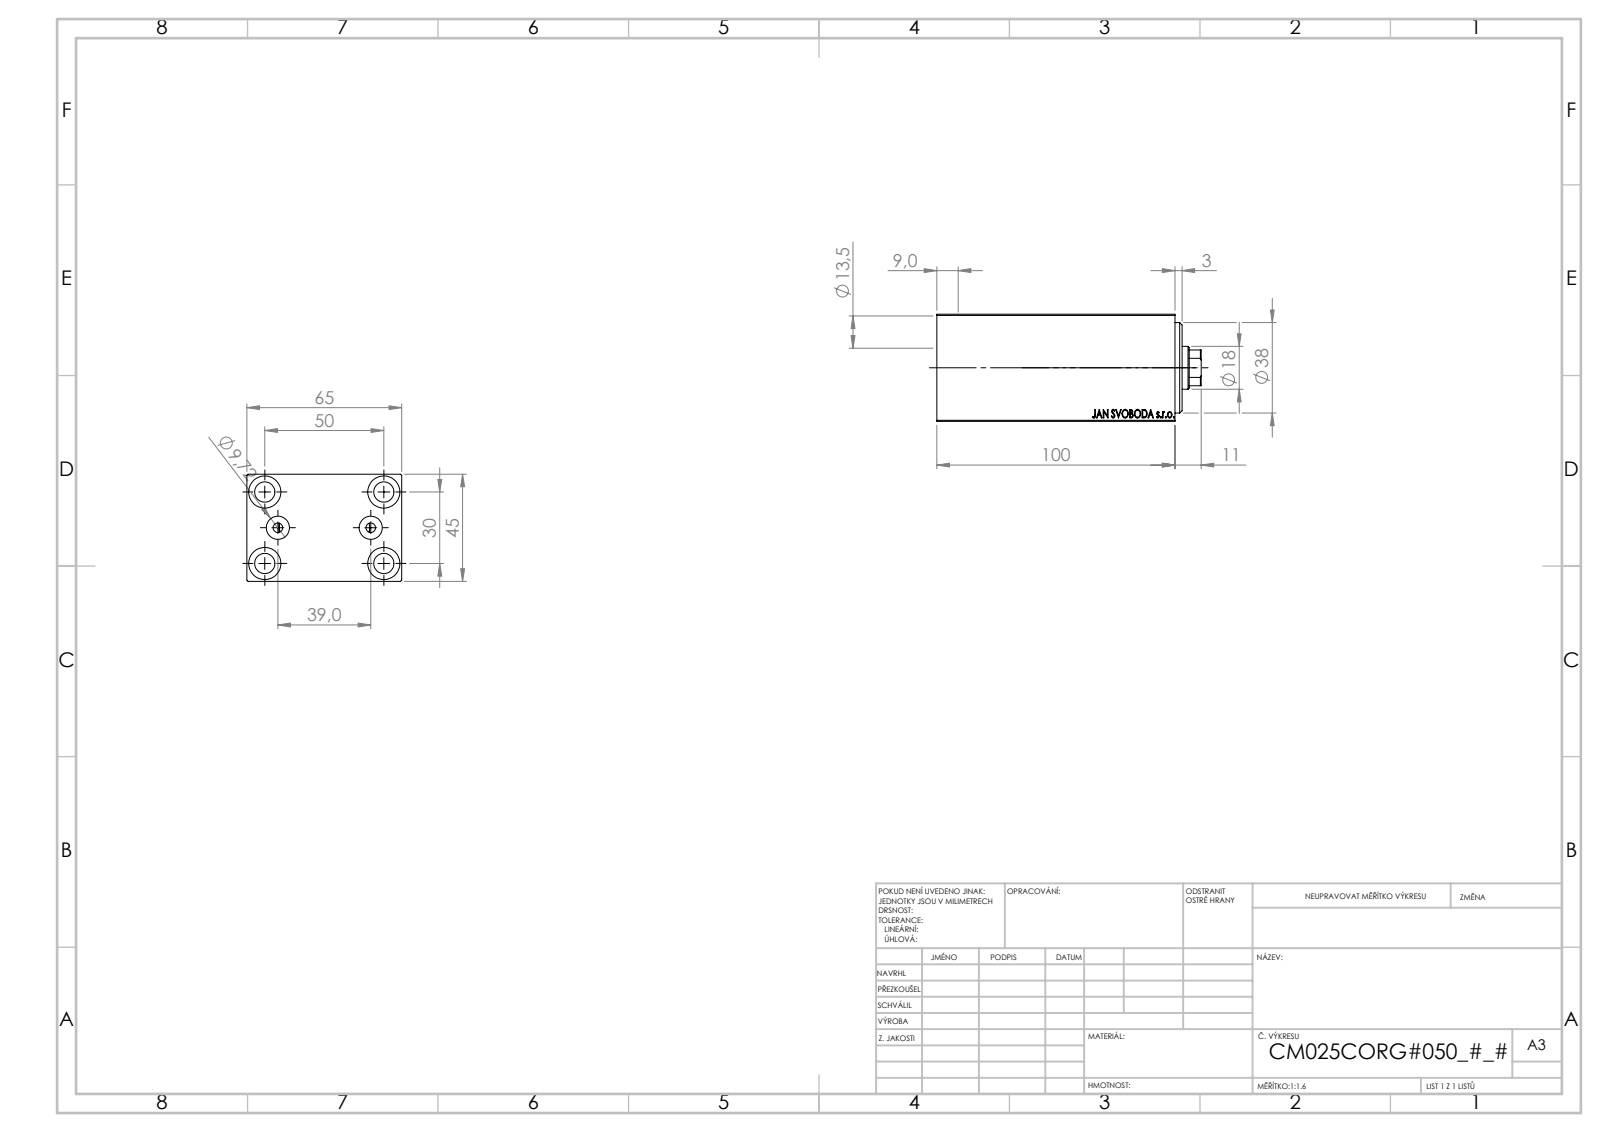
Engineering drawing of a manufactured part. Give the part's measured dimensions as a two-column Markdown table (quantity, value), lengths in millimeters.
| quantity | value |
| --- | --- |
| part name | V450CM_C_VCP; V450CM_C_Body; V450CM_VC_B |
| STEP written by | SolidWorks 2019 (CONFIG_CONTROL_DESIGN) |
| units | millimeters |
| bodies | 3 solids, 858 faces (408 planar, 56 cylindrical, 394 other) |
| overall size | 111 × 65 × 45 |
| volume | 252 071 mm³ |
| surface area | 63 078 mm² |
| round holes (diameter × count) | 8.5 × 5, 13.5 × 4, 4 × 2, 9.72 × 2, 18 × 1, 21.5 × 1, 25 × 1, 27 × 1, 38 × 1 |
| partial cylindrical surfaces (radius × count) | 8.5 × 1 |
| main face-to-face distances | 45, 65, 94, 95, 5, 100, 3, 6, 89, 8 |
| hole center spacings | 15.98, 29.15, 46.96, 19.5, 30, 50, 58.31, 39 |
